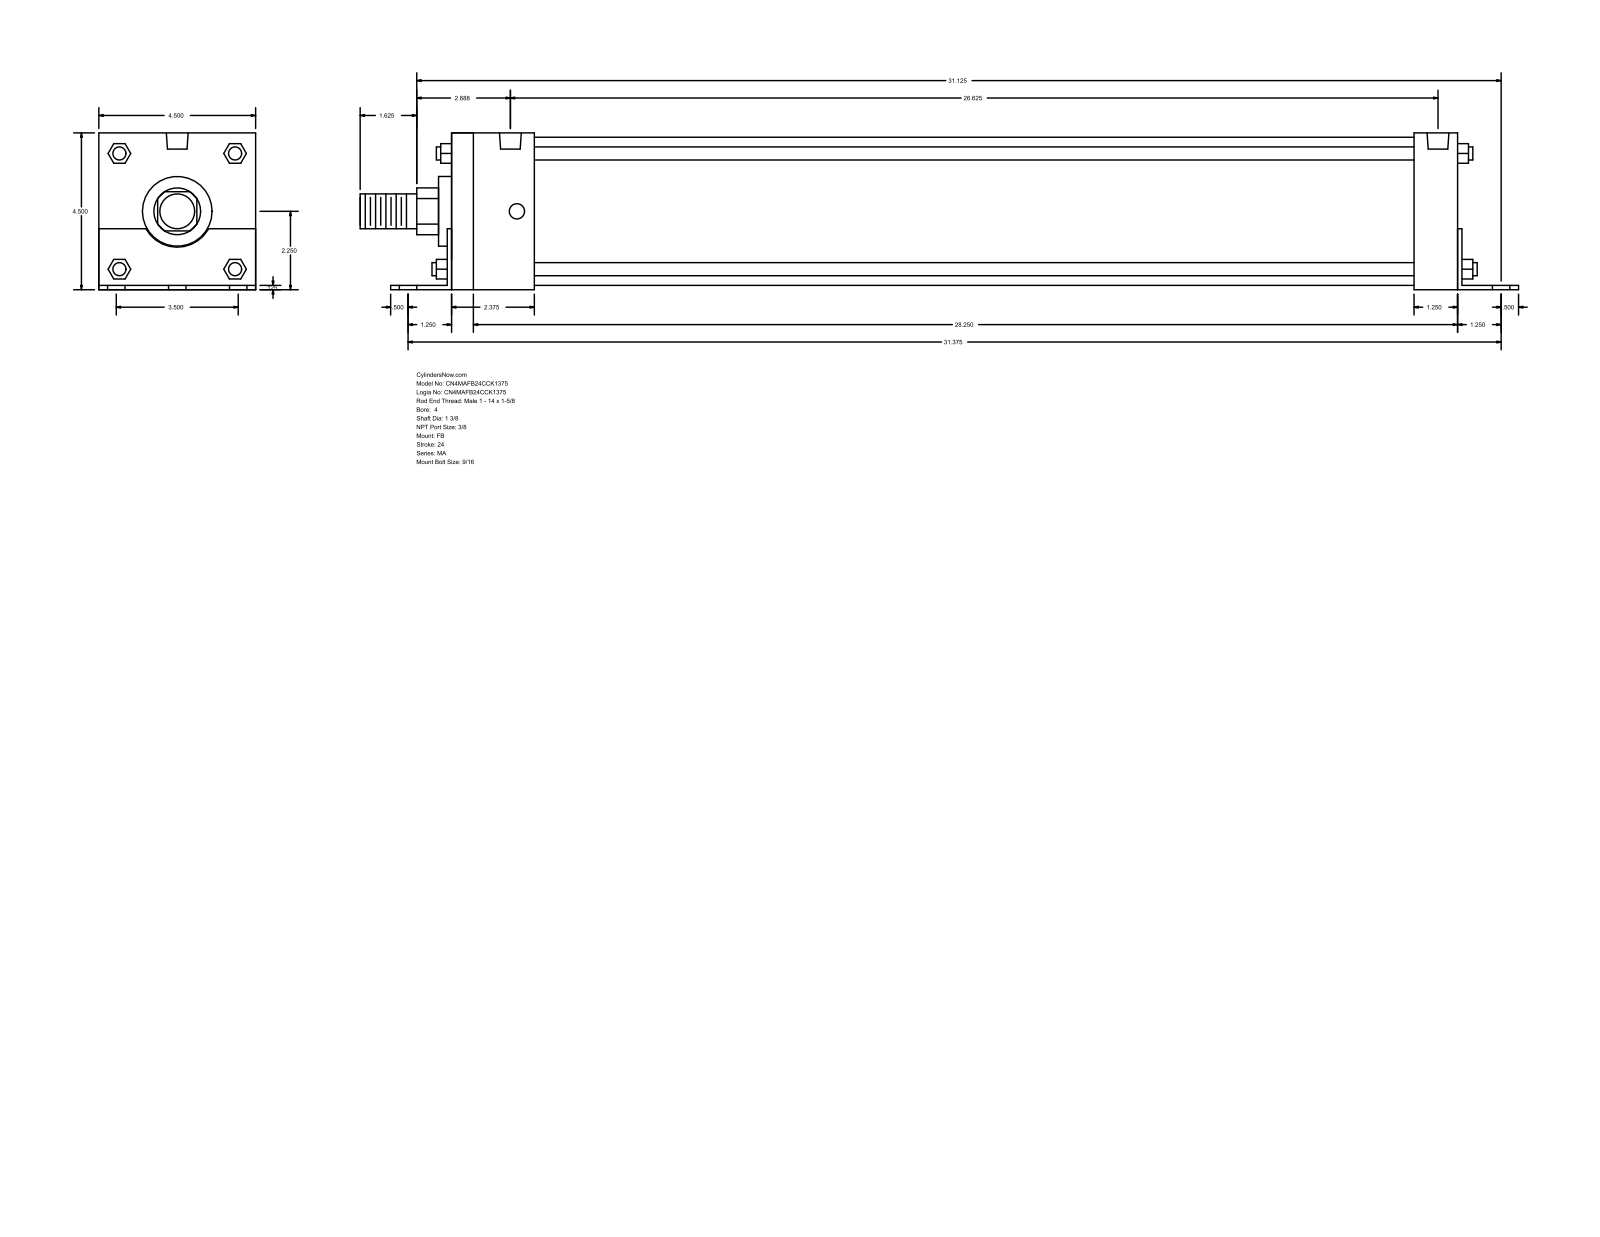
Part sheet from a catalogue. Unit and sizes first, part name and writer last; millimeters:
Units: millimetres
Overall size (bounding box): 844.55 × 114.35 × 114.3
Round holes (diameter × count): ⌀14.29 ×6, ⌀11.11 ×4, ⌀15.93 ×2
Round bosses / shafts (diameter × count): ⌀9.53 ×4, ⌀107.95 ×1, ⌀50.8 ×1, ⌀34.92 ×1, ⌀25.4 ×1
Partial cylindrical surfaces — rounded edges, fillets, slot ends (radius × count): R17.06 ×1, R26.16 ×1
Main face-to-face distances: 114.3, 3.17, 114.35, 3.12, 111.18, 736.6, 733.43, 739.77, 31.75, 704.85
Hole centre spacings: 44.45, 798.17, 796.93, 4.77, 64, 67.51, 86.85, 88.9
Bodies: 0 solids, 140 faces (105 planar, 35 cylindrical, 0 other)
Part name (STEP PRODUCT): MA_FB__0400_1.375
STEP written by: GSSL Pune (CONFIG_CONTROL_DESIGN)
